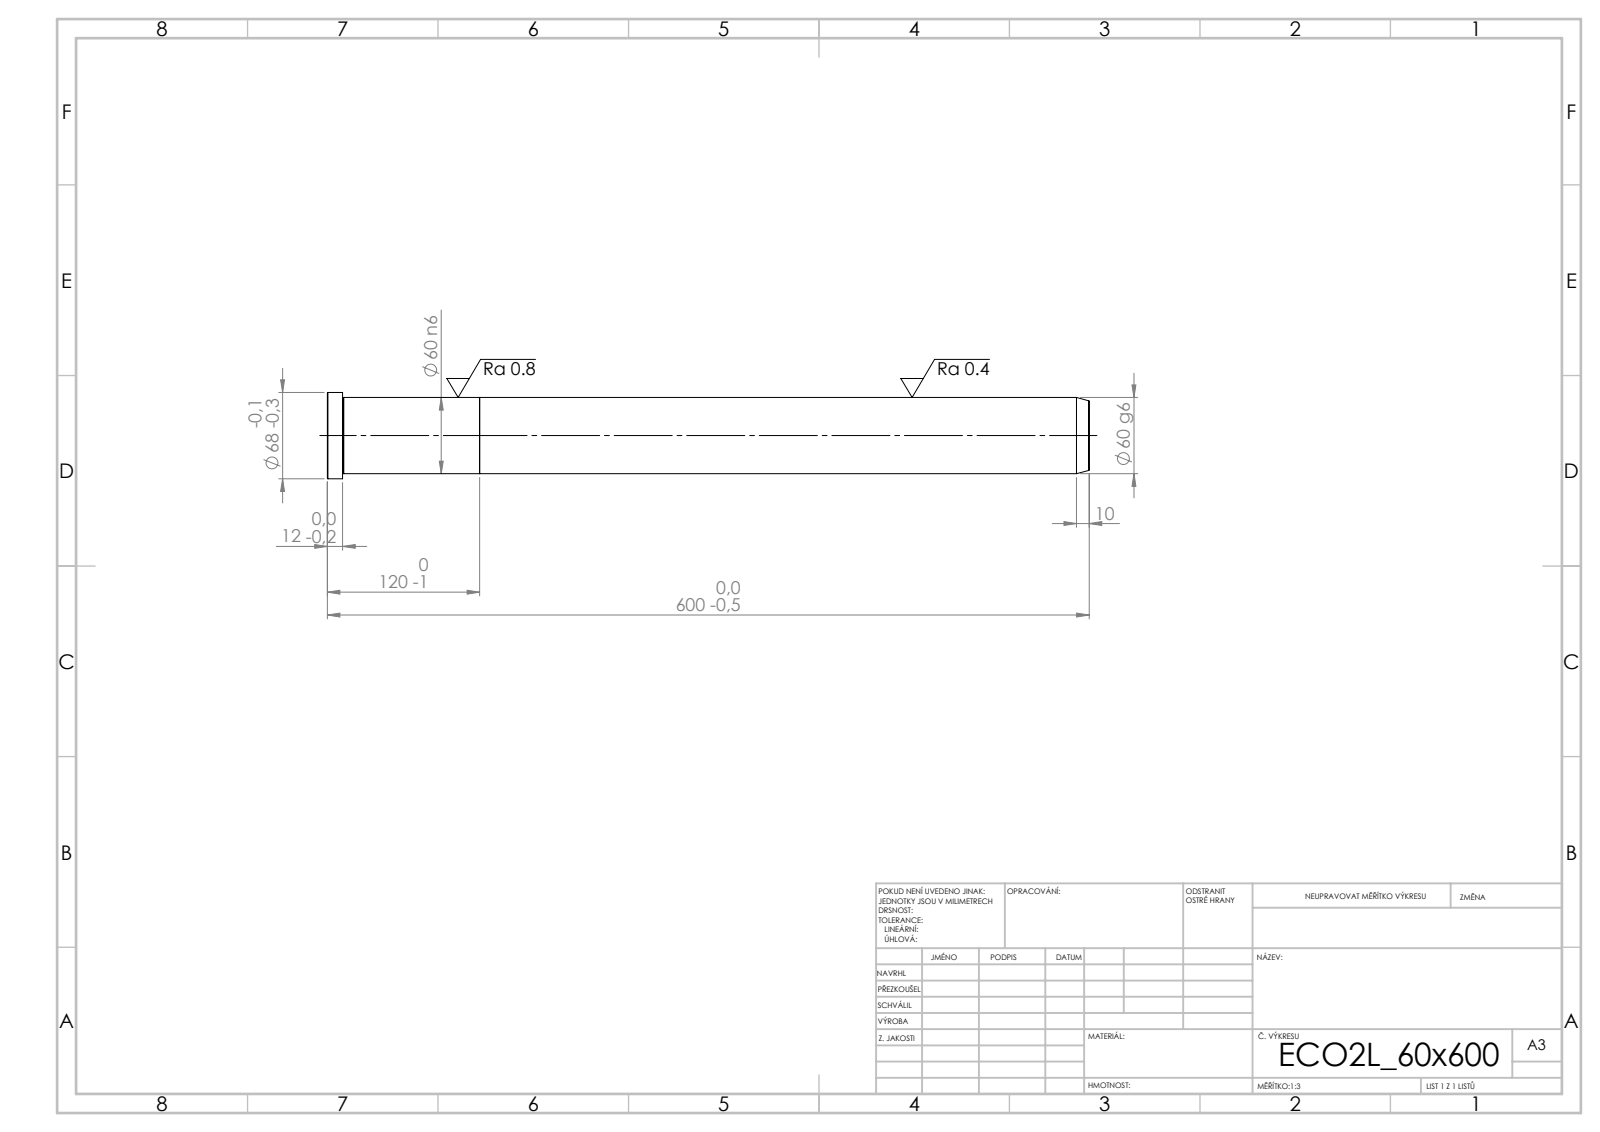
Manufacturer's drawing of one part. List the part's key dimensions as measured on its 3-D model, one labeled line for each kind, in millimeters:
STEP written by: SolidWorks 2019 (CONFIG_CONTROL_DESIGN)
Units: millimetres
Bodies: 2 solids, 21 faces (5 planar, 6 cylindrical, 10 other)
Overall size (bounding box): 600 × 68 × 68
Volume: 1 704 000 mm³ · Surface area: 125 836 mm²
Round bosses / shafts (diameter × count): ⌀68 ×1, ⌀60 ×1
Main face-to-face distances: 120, 480, 600, 588, 108, 12
